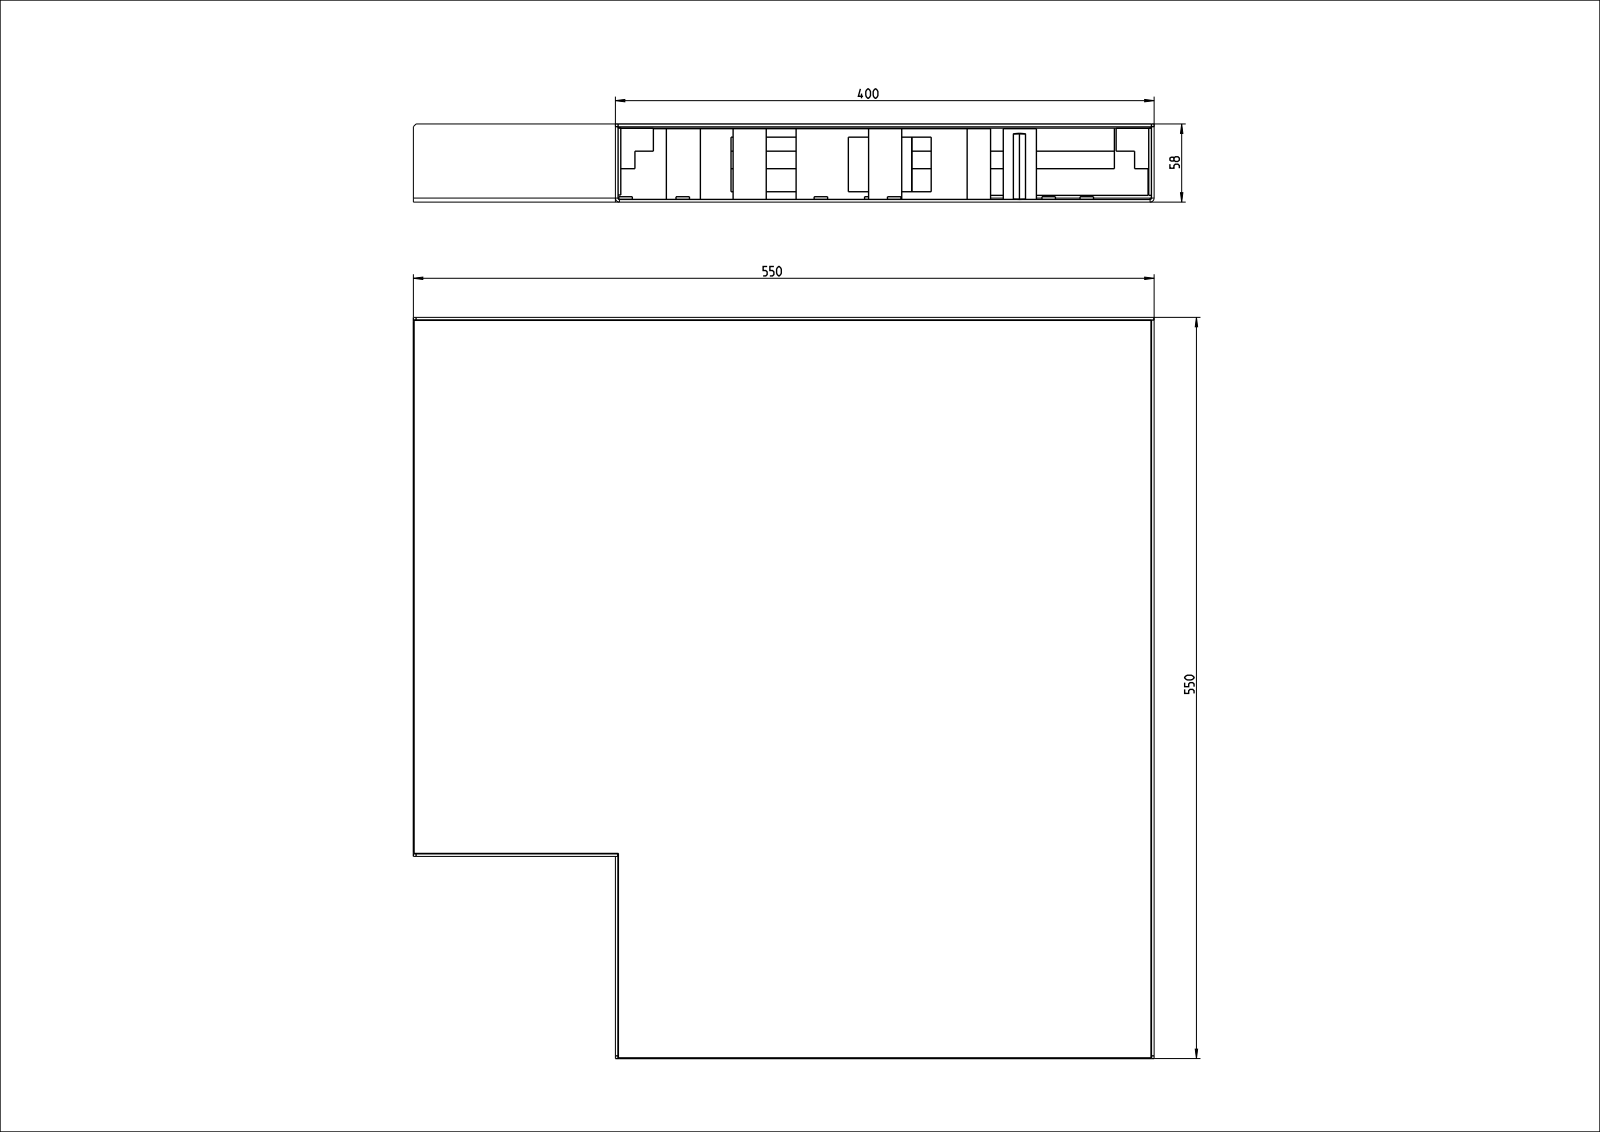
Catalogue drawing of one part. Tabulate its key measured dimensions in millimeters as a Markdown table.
| quantity | value |
| --- | --- |
| part name | T-01226; T-01219; T-01248; T-01247 (+8 more) |
| STEP written by | CREO PARAMETRIC BY PTC INC, 2022024 (AUTOMOTIVE_DESIGN) |
| units | millimeters |
| bodies | 18 solids, 456 faces (299 planar, 105 cylindrical, 52 other) |
| overall size | 713.76 × 655.09 × 58.23 |
| volume | 3 153 000 mm³ |
| surface area | 1 928 000 mm² |
| round holes (diameter × count) | 6 × 12, 6.5 × 8, 13.6 × 7 |
| round bosses / shafts (diameter × count) | 10 × 12 |
| partial cylindrical surfaces (radius × count) | 0.1 × 4, 1 × 4, 3 × 4 |
| main face-to-face distances | 2, 52.8, 1, 53.8, 54.8, 55.8, 4, 396, 394, 7.8 |
| hole center spacings | 20, 300, 315.47, 97.57, 300.67, 212.6, 33, 53 |
